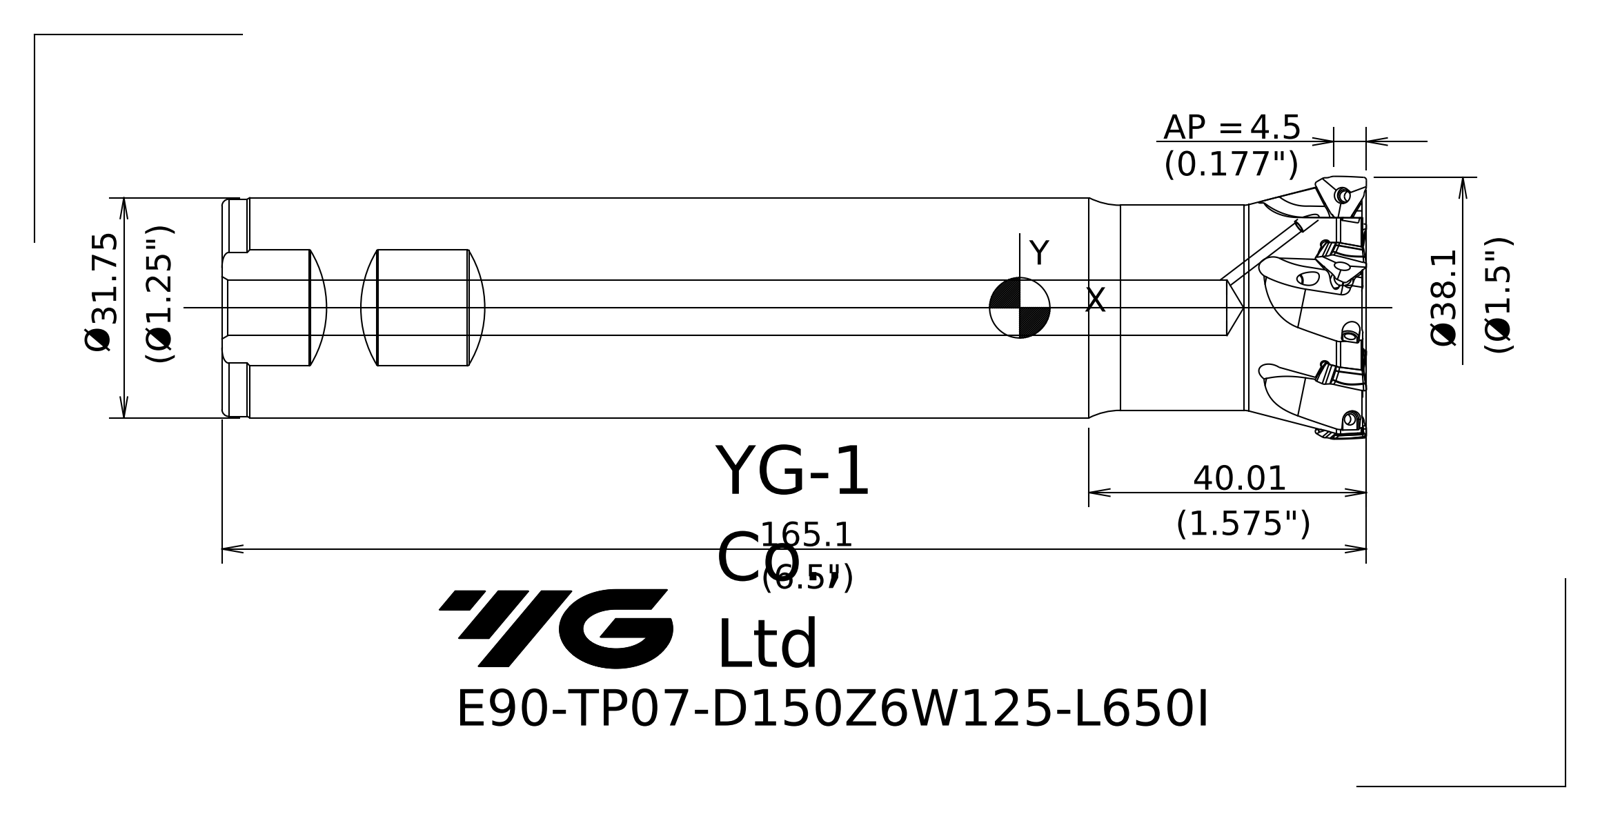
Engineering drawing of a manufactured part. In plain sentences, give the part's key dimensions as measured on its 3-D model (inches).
The part is named "10220928B8670h8p". Its 3-D file was written by "SIEMENS PLM Software NX 10.0 (AP203_CONFIGURATION_CONTROLLED_3D_DESIGN_OF_MECHANICAL_PARTS_AND_ASSEMBLIES_MIM_LF)". It is 1 solid with 51 faces: 8 planar, 8 cylindrical and 35 other. Overall it measures 6.5 by 1.502 by 1.502 inches. Its volume is 7.417 cubic inches and its surface area 37.46 square inches. Round holes: 1 of diameter 0.059, 1 of diameter 0.315. Round bosses or shafts: 1 of diameter 1.25, 1 of diameter 1.234, 1 of diameter 1.165. Partial cylindrical surfaces (rounded edges, fillets, slot ends): 3 of radius 0.012. The main face-to-face distances are 6.474, 6.48, 0.635.
